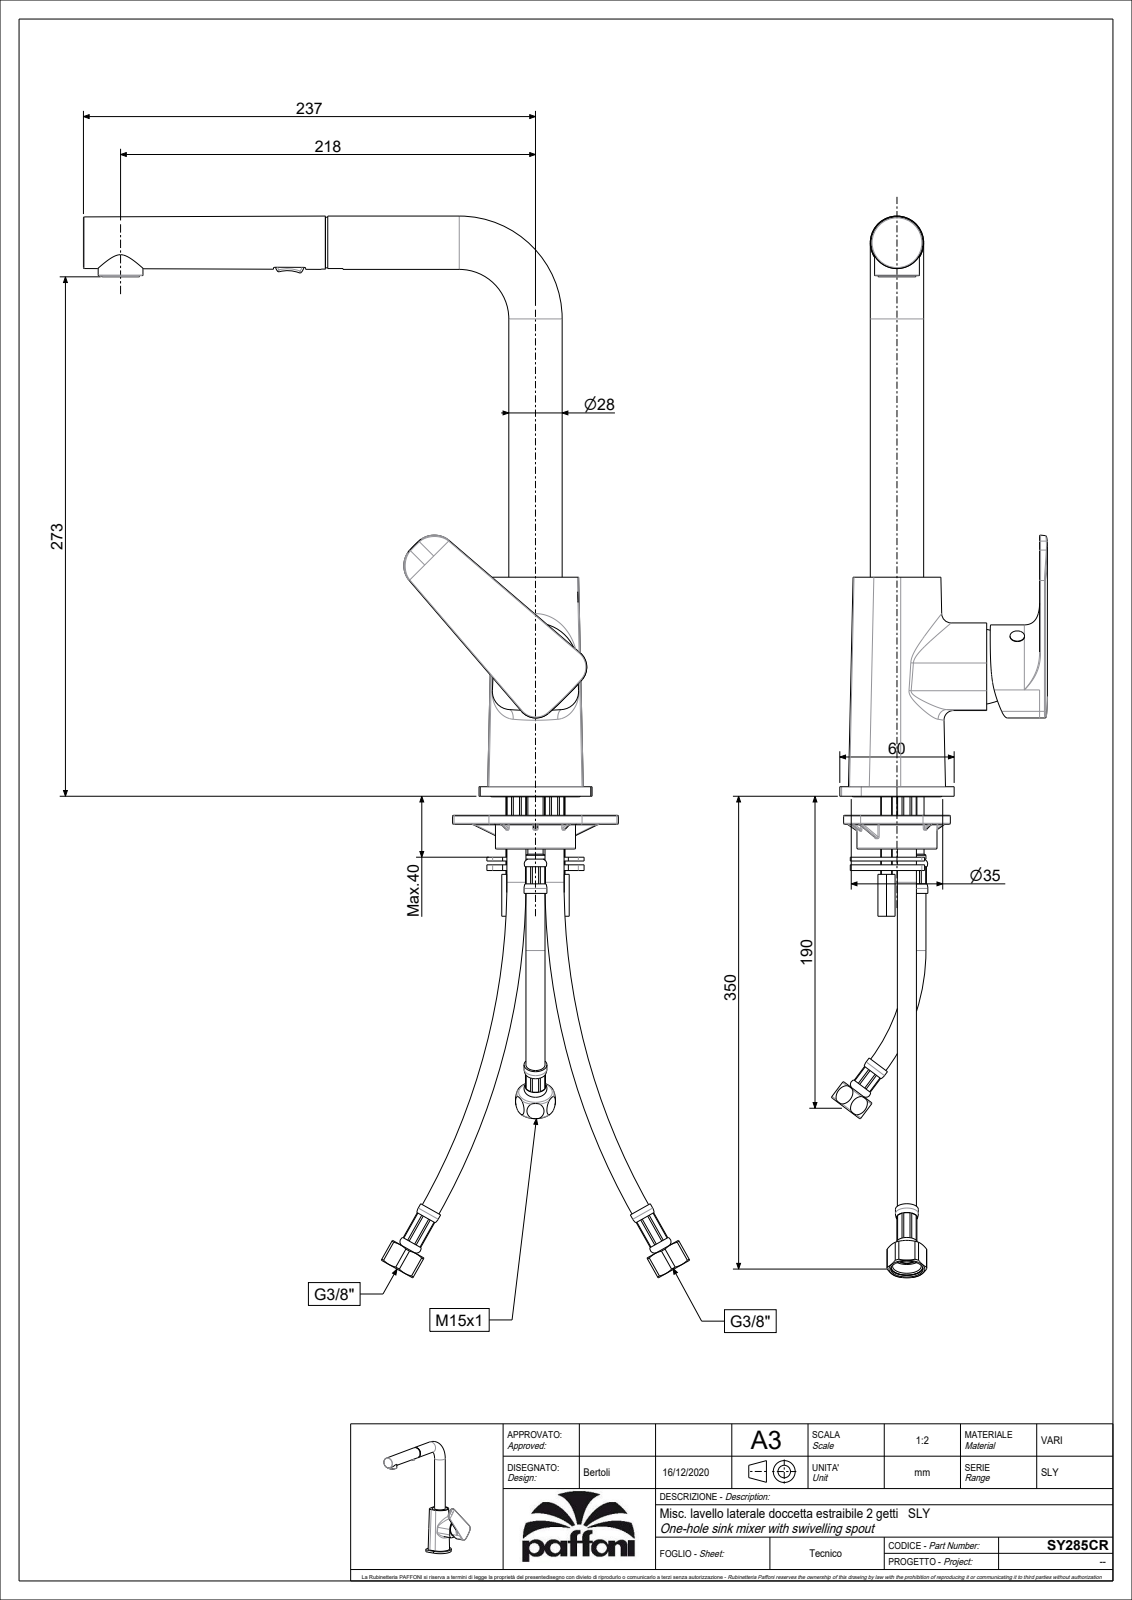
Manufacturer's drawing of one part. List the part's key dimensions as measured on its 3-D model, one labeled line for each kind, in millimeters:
Part name (STEP PRODUCT): SY285CR
STEP written by: CREO PARAMETRIC BY PTC INC, 2020044 (CONFIG_CONTROL_DESIGN)
Units: millimetres
Bodies: 2 solids, 2038 faces (1027 planar, 545 cylindrical, 466 other)
Overall size (bounding box): 304.6 × 267.64 × 108.92
Volume: 346 675 mm³ · Surface area: 157 849 mm²
Round holes (diameter × count): ⌀7 ×6, ⌀5.5 ×3, ⌀8.6 ×3, ⌀9.4 ×3, ⌀5 ×2, ⌀8 ×2, ⌀25 ×2, ⌀38 ×2, ⌀40 ×2, ⌀3 ×1, ⌀3.3 ×1, ⌀3.4 ×1
Round bosses / shafts (diameter × count): ⌀28 ×2, ⌀4.8 ×2, ⌀4 ×2, ⌀44.5 ×1, ⌀39.8 ×1, ⌀36.8 ×1, ⌀35.4 ×1, ⌀35 ×1
Partial cylindrical surfaces — rounded edges, fillets, slot ends (radius × count): R0.5 ×44, R1.5 ×13, R1 ×12, R3 ×10, R1.7 ×6, R2 ×5, R0.2 ×4, R0.8 ×4
Main face-to-face distances: 2, 7, 5.5, 2.2, 5, 1.5, 2.8, 9.8, 7.5, 15.3
Hole centre spacings: 8.61, 10.99, 11.27, 11.32, 12.5, 13.46, 13.66, 14.65
